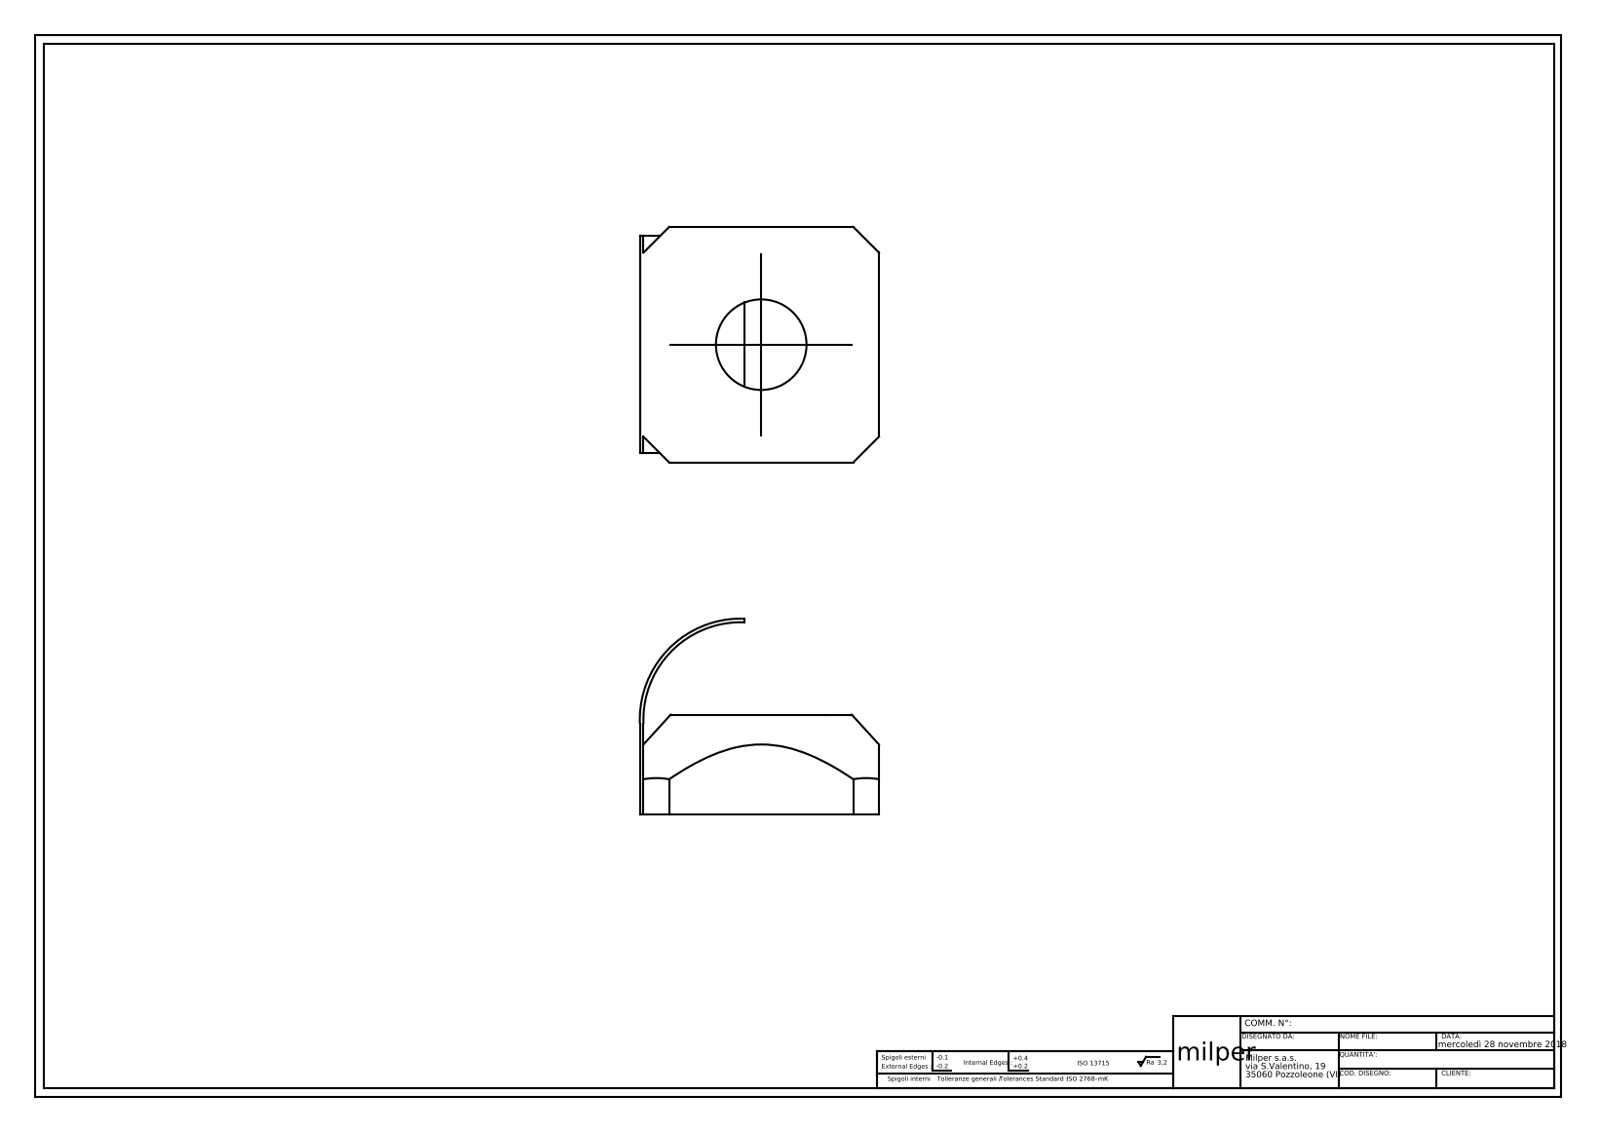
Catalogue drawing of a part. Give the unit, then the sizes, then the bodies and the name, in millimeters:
Units: millimetres
Overall size (bounding box): 13.21 × 13 × 10.8
Round holes (diameter × count): ⌀5 ×1
Partial cylindrical surfaces — rounded edges, fillets, slot ends (radius × count): R2 ×2, R5.37 ×1, R5.57 ×1
Main face-to-face distances: 13, 5.5, 13.2, 16.38, 0.5, 12.5, 12, 5.8, 5.6, 7.4
Volume: 710 mm³ · Surface area: 844 mm²
Bodies: 1 solid, 22 faces (14 planar, 6 cylindrical, 2 other)
Part name (STEP PRODUCT): dado-M5-molla-3D
STEP written by: SolidWorks 2018 (CONFIG_CONTROL_DESIGN)
